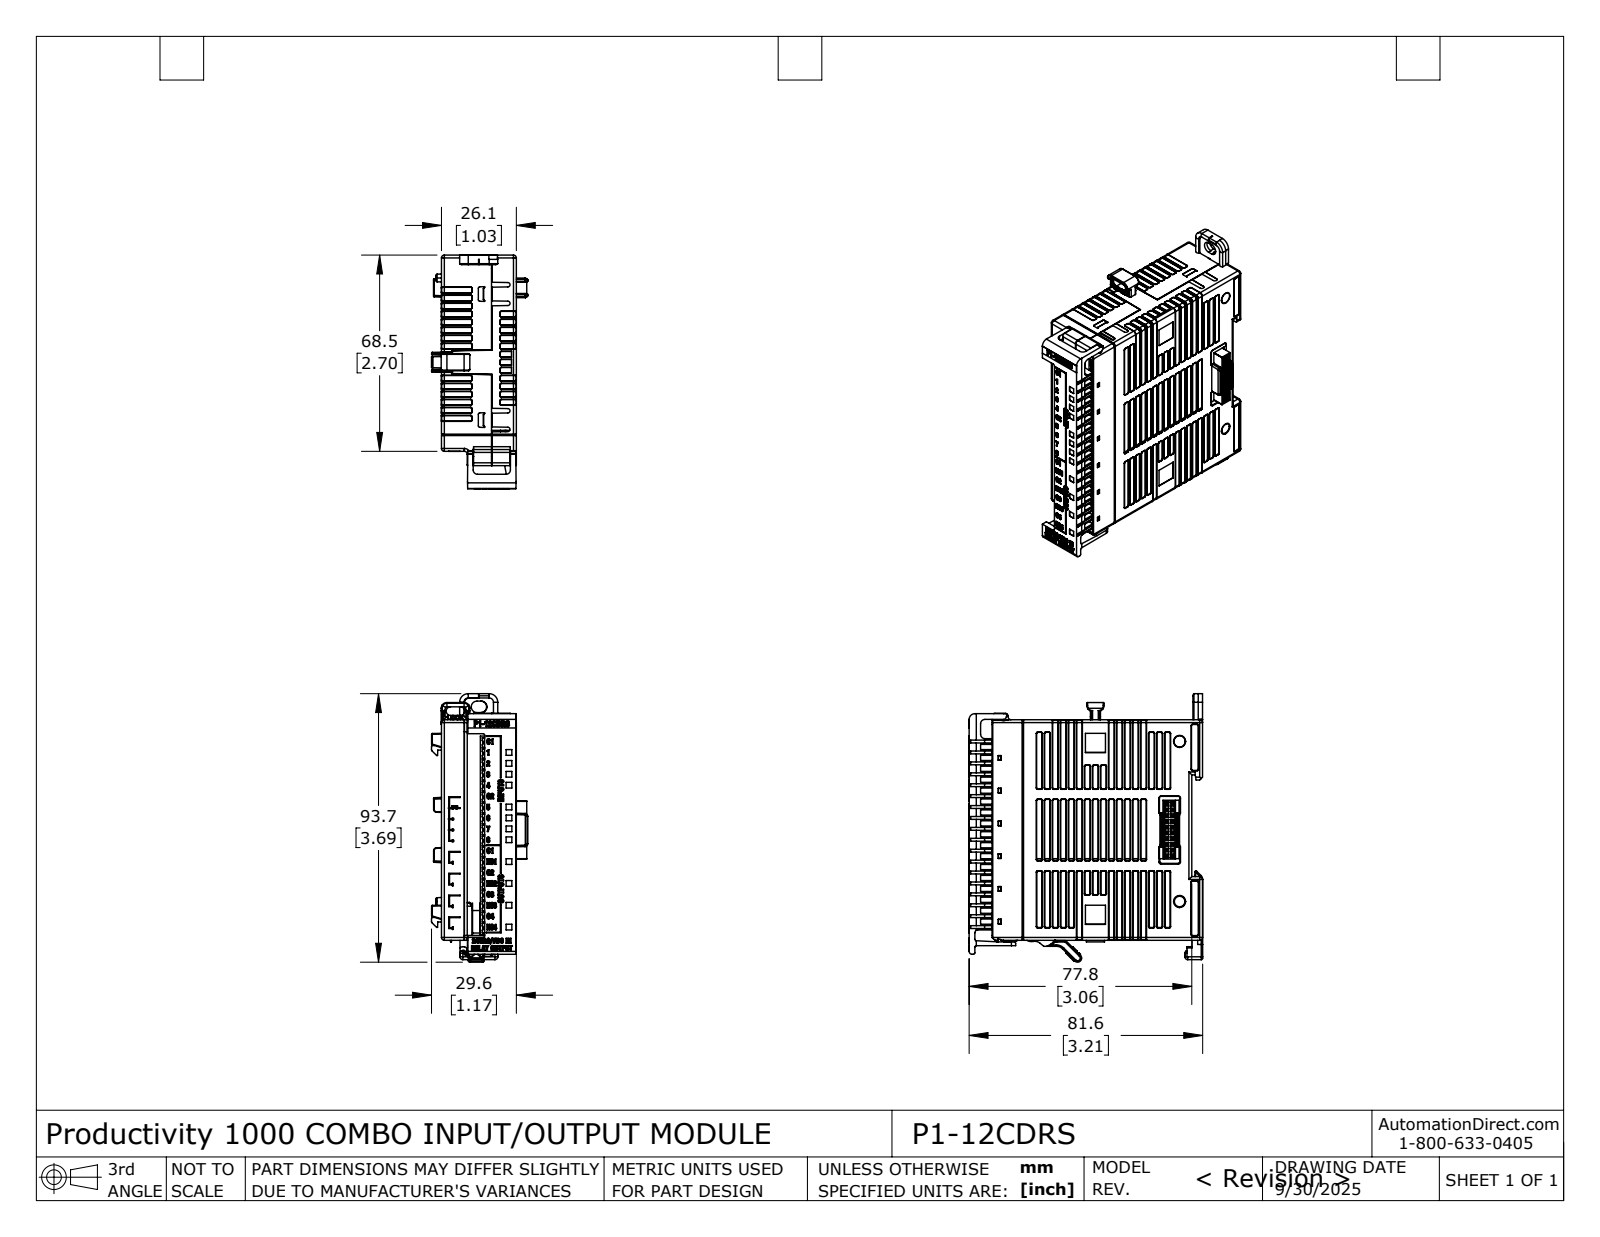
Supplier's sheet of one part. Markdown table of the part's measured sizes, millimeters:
| quantity | value |
| --- | --- |
| part name | P1-12CDRS |
| STEP written by | SolidWorks 2024 (AUTOMOTIVE_DESIGN) |
| units | millimeters |
| bodies | 53 solids, 6132 faces (3220 planar, 1380 cylindrical, 1532 other) |
| overall size | 93.7 × 81.6 × 33.6 |
| volume | 47 590 mm³ |
| surface area | 47 240 mm² |
| round holes (diameter × count) | 0.3 × 20, 0.6 × 8, 0.4 × 5, 1.2 × 1, 1.8 × 1 |
| round bosses / shafts (diameter × count) | 0.8 × 5, 1.6 × 1 |
| partial cylindrical surfaces (radius × count) | 0.3 × 254, 0.5 × 120, 0.3 × 114, 0.2 × 84, 1 × 75, 1.6 × 18, 2 × 14, 1.5 × 11 |
| main face-to-face distances | 1.5, 24.6, 23.1, 26.2, 75.5, 1.5, 26.1, 24.6, 24.4, 45.7 |
| hole center spacings | 2, 2.8, 4, 4.5, 6, 6.3, 8, 8.3 |
